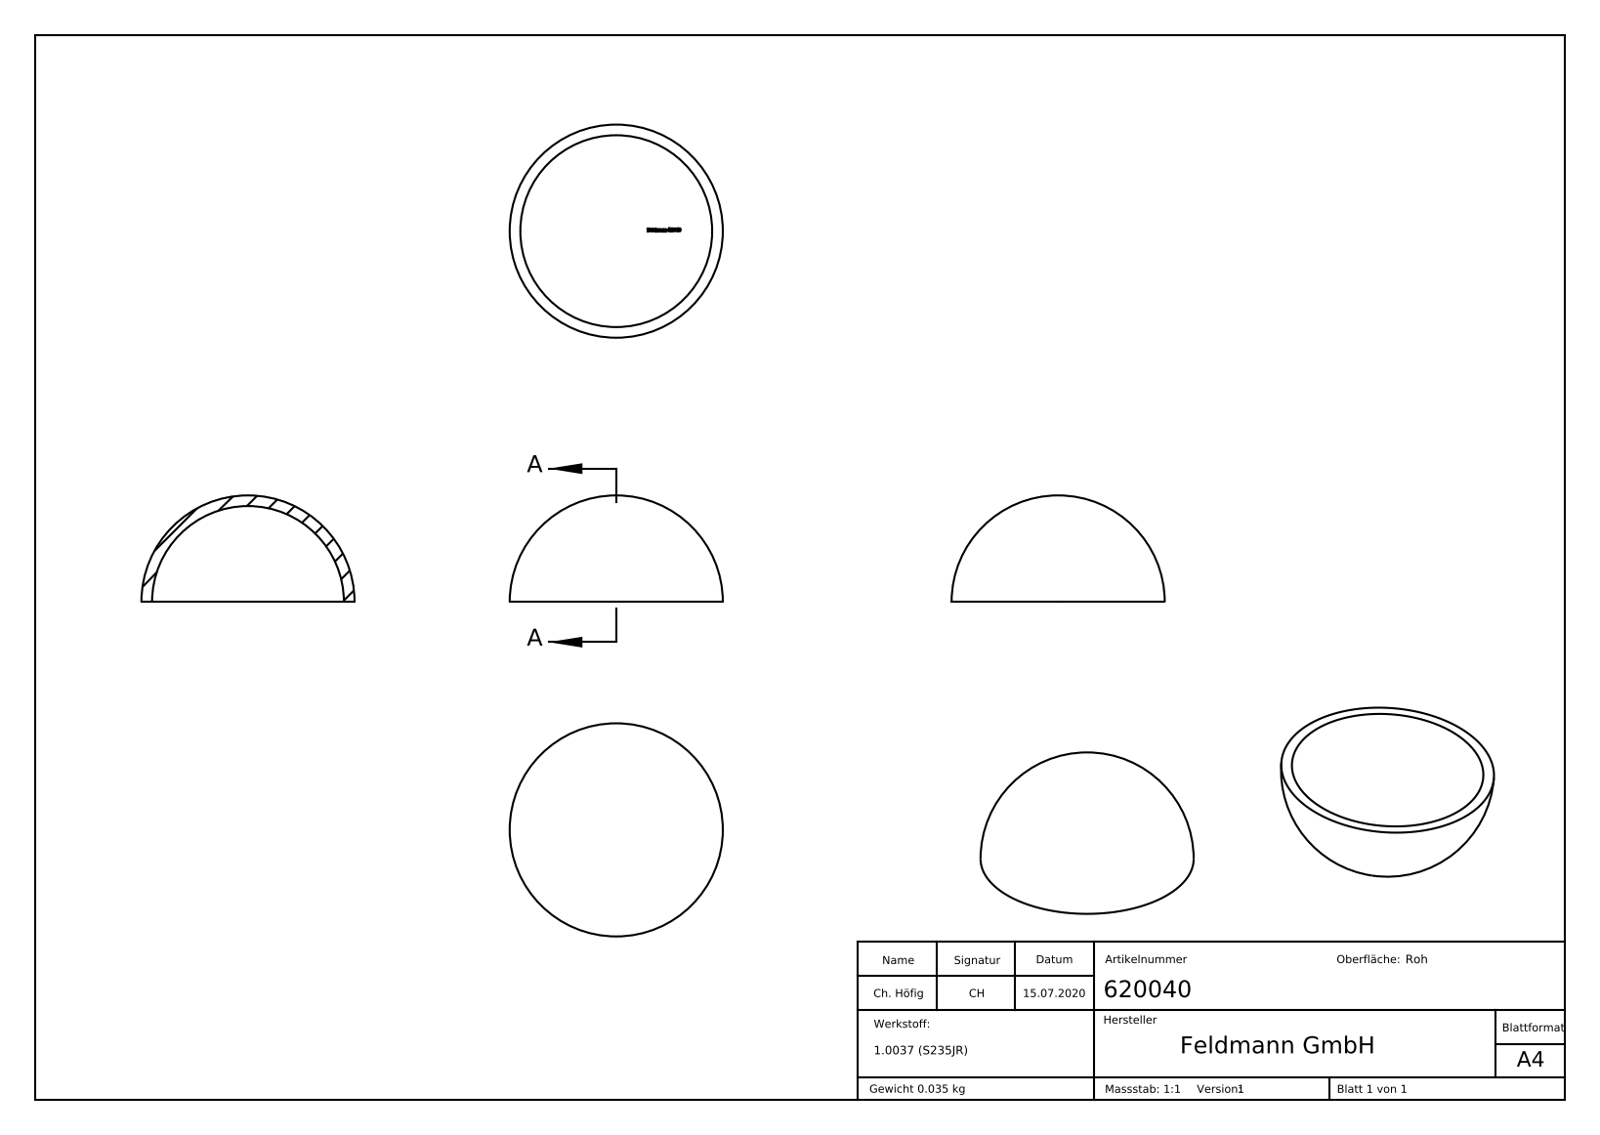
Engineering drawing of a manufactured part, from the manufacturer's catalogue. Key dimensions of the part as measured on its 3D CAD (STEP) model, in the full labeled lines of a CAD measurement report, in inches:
Part name (STEP PRODUCT): 620040
STEP written by: SolidWorks 2018 (CONFIG_CONTROL_DESIGN)
Units: inches
Bodies: 1 solid, 191 faces (77 planar, 0 cylindrical, 114 other)
Overall size (bounding box): 1.575 × 1.575 × 0.787
Volume: 0.277 in³ · Surface area: 7.428 in²
Main face-to-face distances: 0.047, 0.022, 0.02, 0.122, 0.098, 0.189, 0.032, 0.169, 0.026, 0.22
